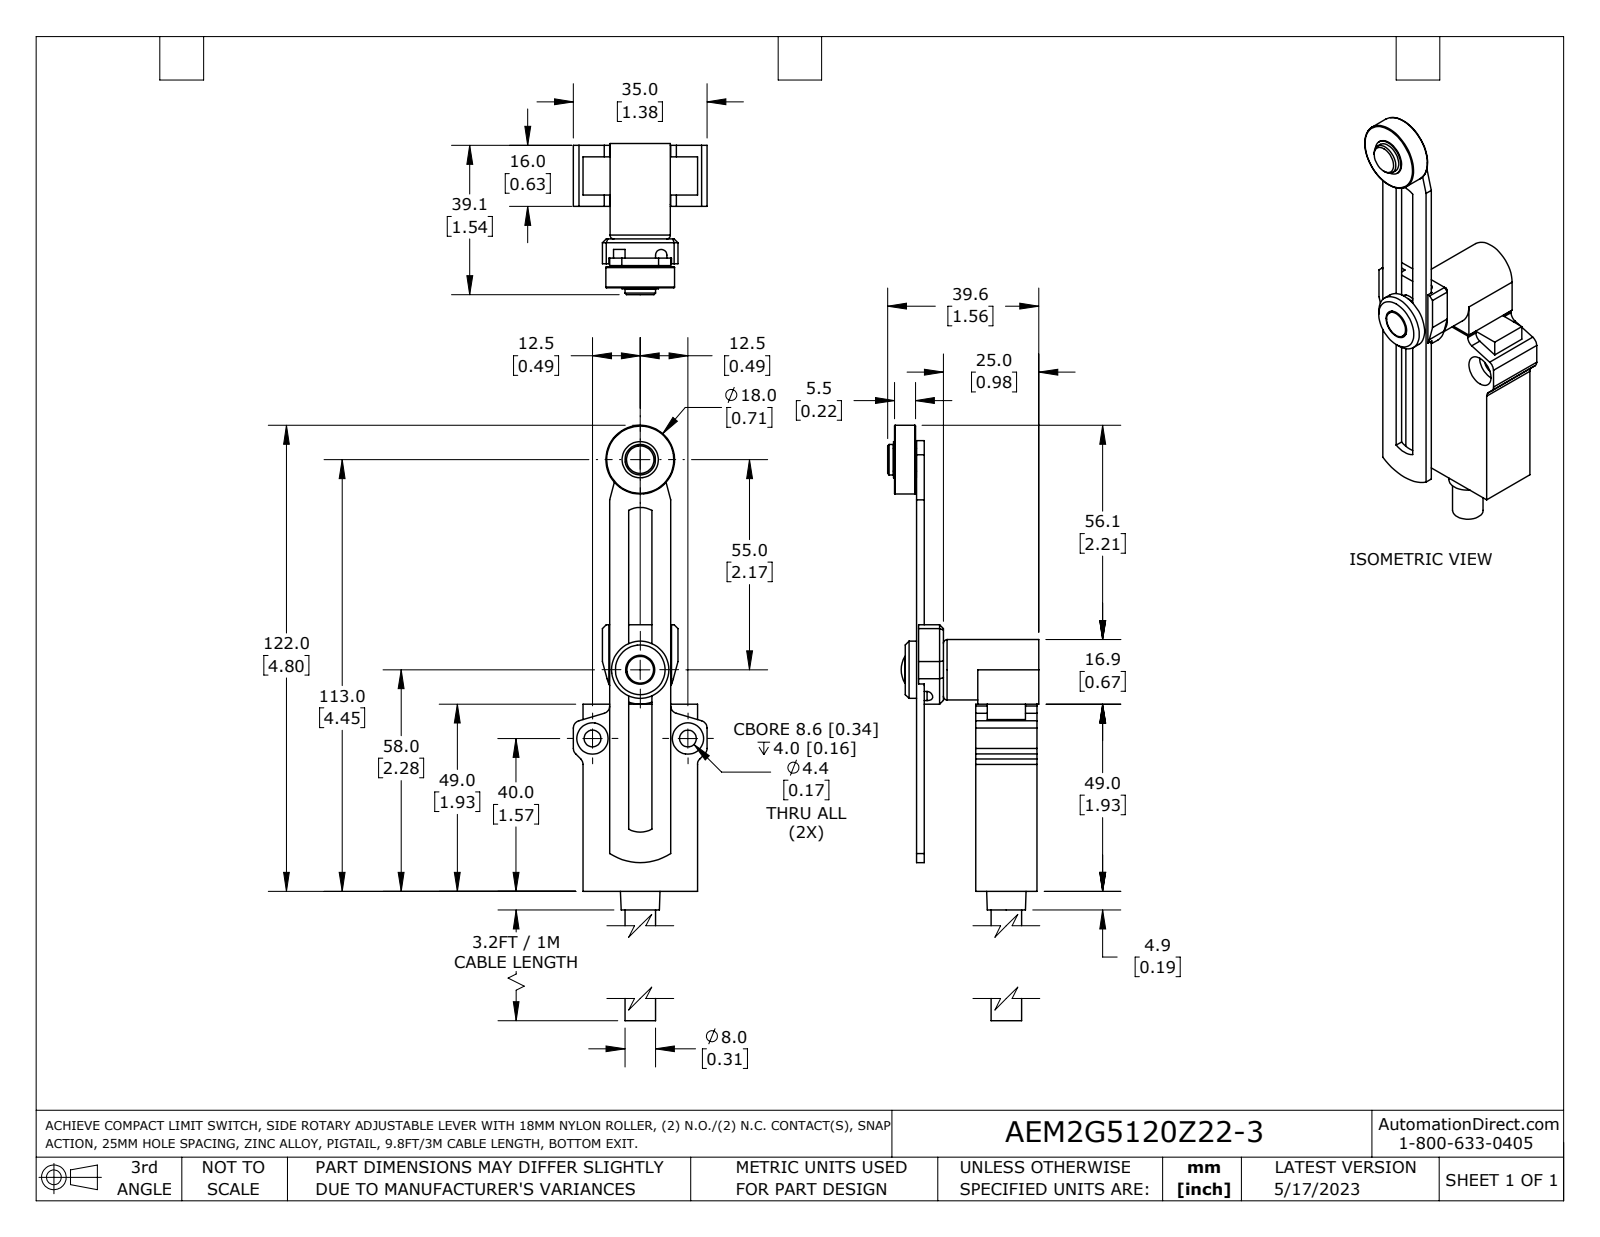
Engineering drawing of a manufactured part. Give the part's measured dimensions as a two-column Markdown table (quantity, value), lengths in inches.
| quantity | value |
| --- | --- |
| part name | AEM2G5120Z22-3 |
| STEP written by | SolidWorks 2021 (AUTOMOTIVE_DESIGN) |
| units | inches |
| bodies | 1 solid, 151 faces (100 planar, 43 cylindrical, 8 other) |
| overall size | 5.39 × 1.559 × 1.378 |
| volume | 2.102 in³ |
| surface area | 21.7 in² |
| round holes (diameter × count) | 0.173 × 2, 0.323 × 2, 0.197 × 1, 0.299 × 1, 0.433 × 1 |
| round bosses / shafts (diameter × count) | 0.315 × 2, 0.709 × 1, 0.622 × 1, 0.591 × 1, 0.374 × 1, 0.276 × 1, 0.236 × 1 |
| partial cylindrical surfaces (radius × count) | 0.079 × 8, 0.256 × 3, 0.059 × 1, 0.181 × 1, 0.197 × 1, 0.252 × 1, 0.354 × 1, 0.571 × 1 |
| main face-to-face distances | 0.63, 0.531, 0.61, 0.079, 1.24, 1.161, 1.181, 0.276, 0.906, 0.02 |
| hole center spacings | 0.863, 0.984 |
